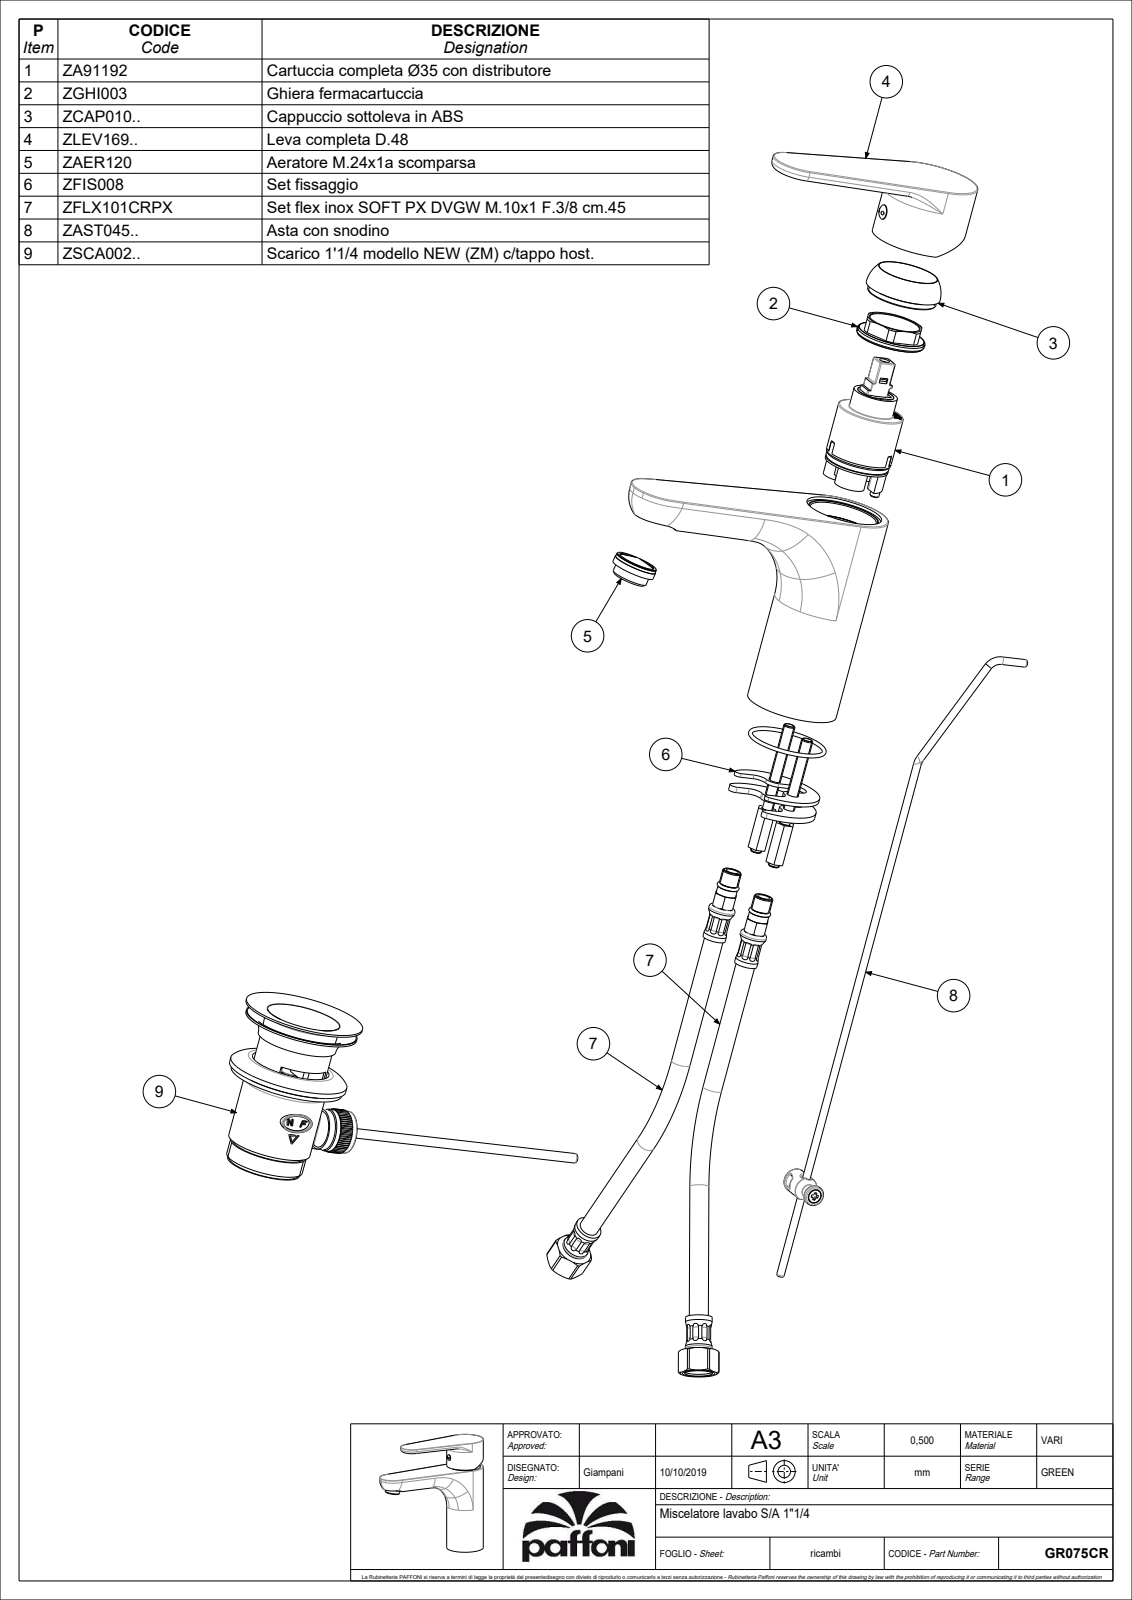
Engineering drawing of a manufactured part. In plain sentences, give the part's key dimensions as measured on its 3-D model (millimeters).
The part is named "GR075CR". Its 3-D file was written by "CREO PARAMETRIC BY PTC INC, 2020044 (CONFIG_CONTROL_DESIGN)". It is 3 solids with 452 faces: 112 planar, 138 cylindrical and 202 other. Overall it measures 177.09 by 147.5 by 48 millimeters. Its volume is 123 696 cubic millimeters and its surface area 83 810 square millimeters. Round holes: 3 of diameter 5, 1 of diameter 3, 1 of diameter 3.5, 1 of diameter 4.2, 1 of diameter 16, 1 of diameter 19.5, 1 of diameter 25, 1 of diameter 31.5, 1 of diameter 33, 1 of diameter 34, 1 of diameter 35.7, 1 of diameter 43. Round bosses or shafts: 2 of diameter 48, 2 of diameter 4, 1 of diameter 38.5, 1 of diameter 23, 1 of diameter 18.8, 1 of diameter 7.6, 1 of diameter 5.5. Partial cylindrical surfaces (rounded edges, fillets, slot ends): 27 of radius 1.5, 16 of radius 1, 8 of radius 6, 4 of radius 0.5, 2 of radius 3, 2 of radius 5, 1 of radius 15, 1 of radius 18.5. The main face-to-face distances are 37.5, 2.5, 40, 6, 34, 31.5, 38, 35.5, 2, 4. The hole center spacings are 12.3, 13.57, 13.6, 13.45, 13.5, 22.
